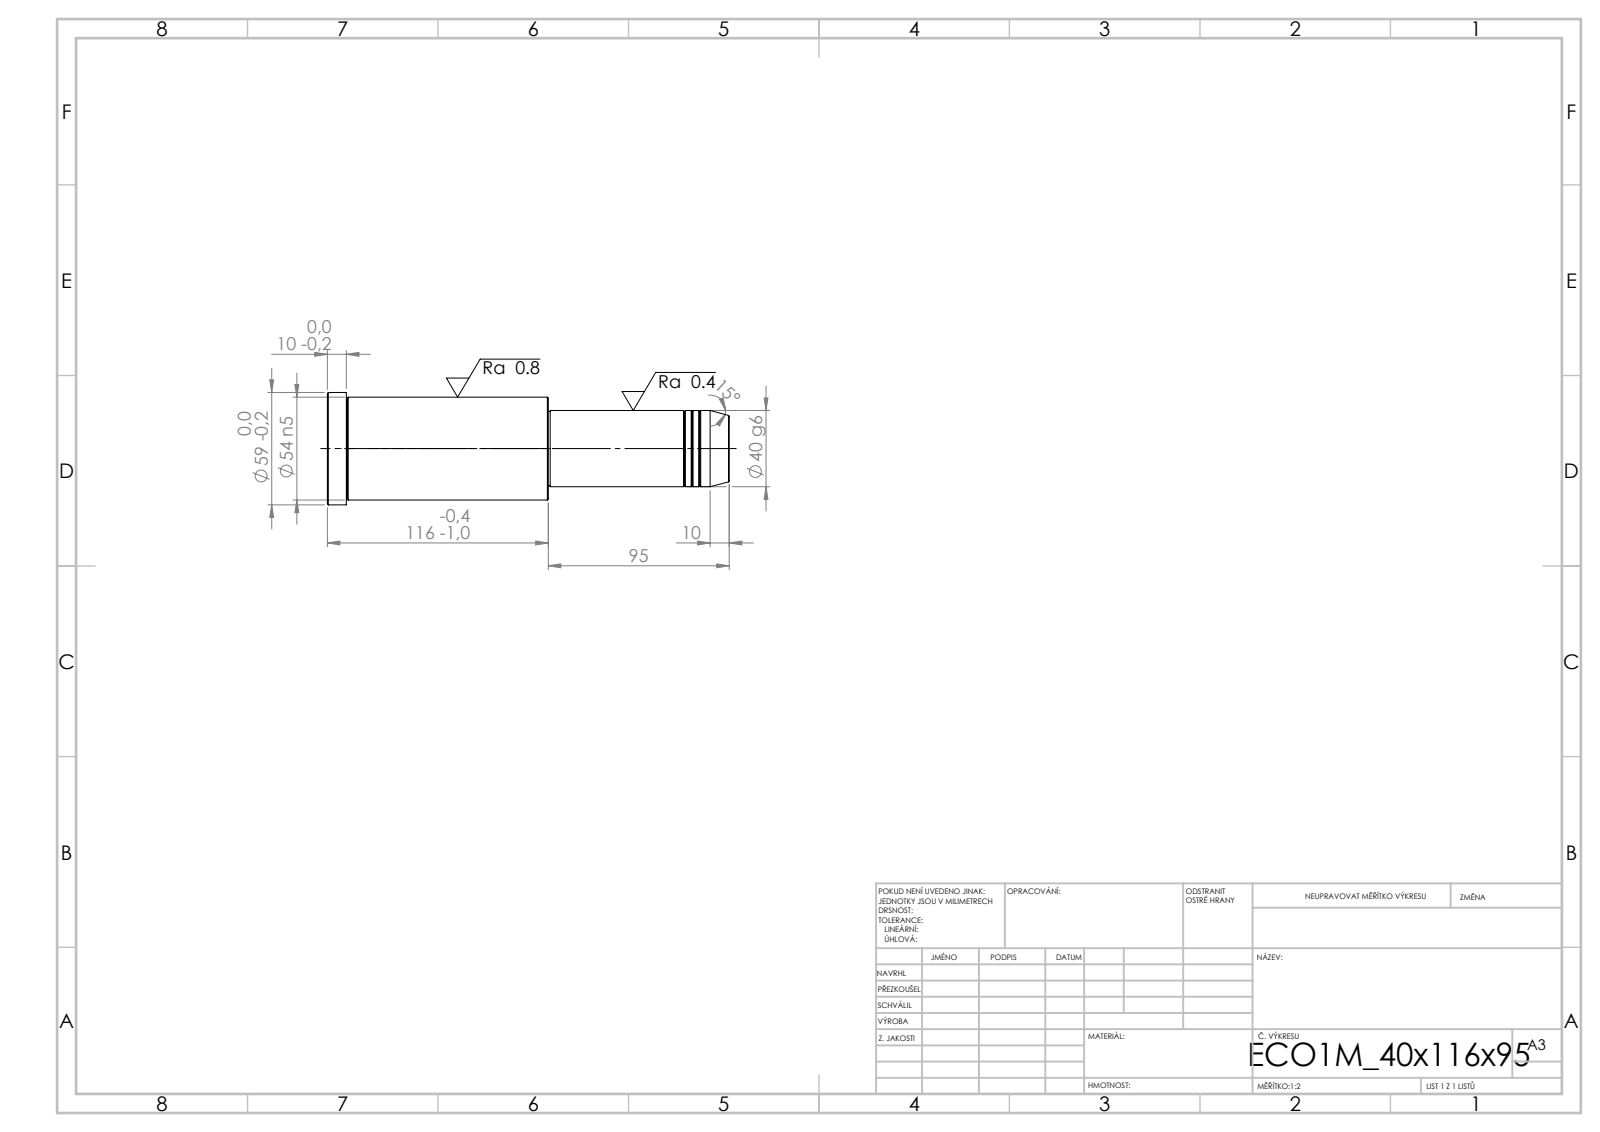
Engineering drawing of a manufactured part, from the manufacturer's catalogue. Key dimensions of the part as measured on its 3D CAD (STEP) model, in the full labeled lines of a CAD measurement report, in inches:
STEP written by: SolidWorks 2019 (CONFIG_CONTROL_DESIGN)
Units: inches
Bodies: 1 solid, 43 faces (5 planar, 14 cylindrical, 24 other)
Overall size (bounding box): 8.307 × 2.323 × 2.323
Volume: 23.65 in³ · Surface area: 57.64 in²
Round bosses / shafts (diameter × count): ⌀2.323 ×1, ⌀2.126 ×1, ⌀1.575 ×1, ⌀1.535 ×1
Main face-to-face distances: 4.567, 3.74, 8.307, 7.913, 4.173, 0.394, 3.701, 0.039, 4.213, 4.606
